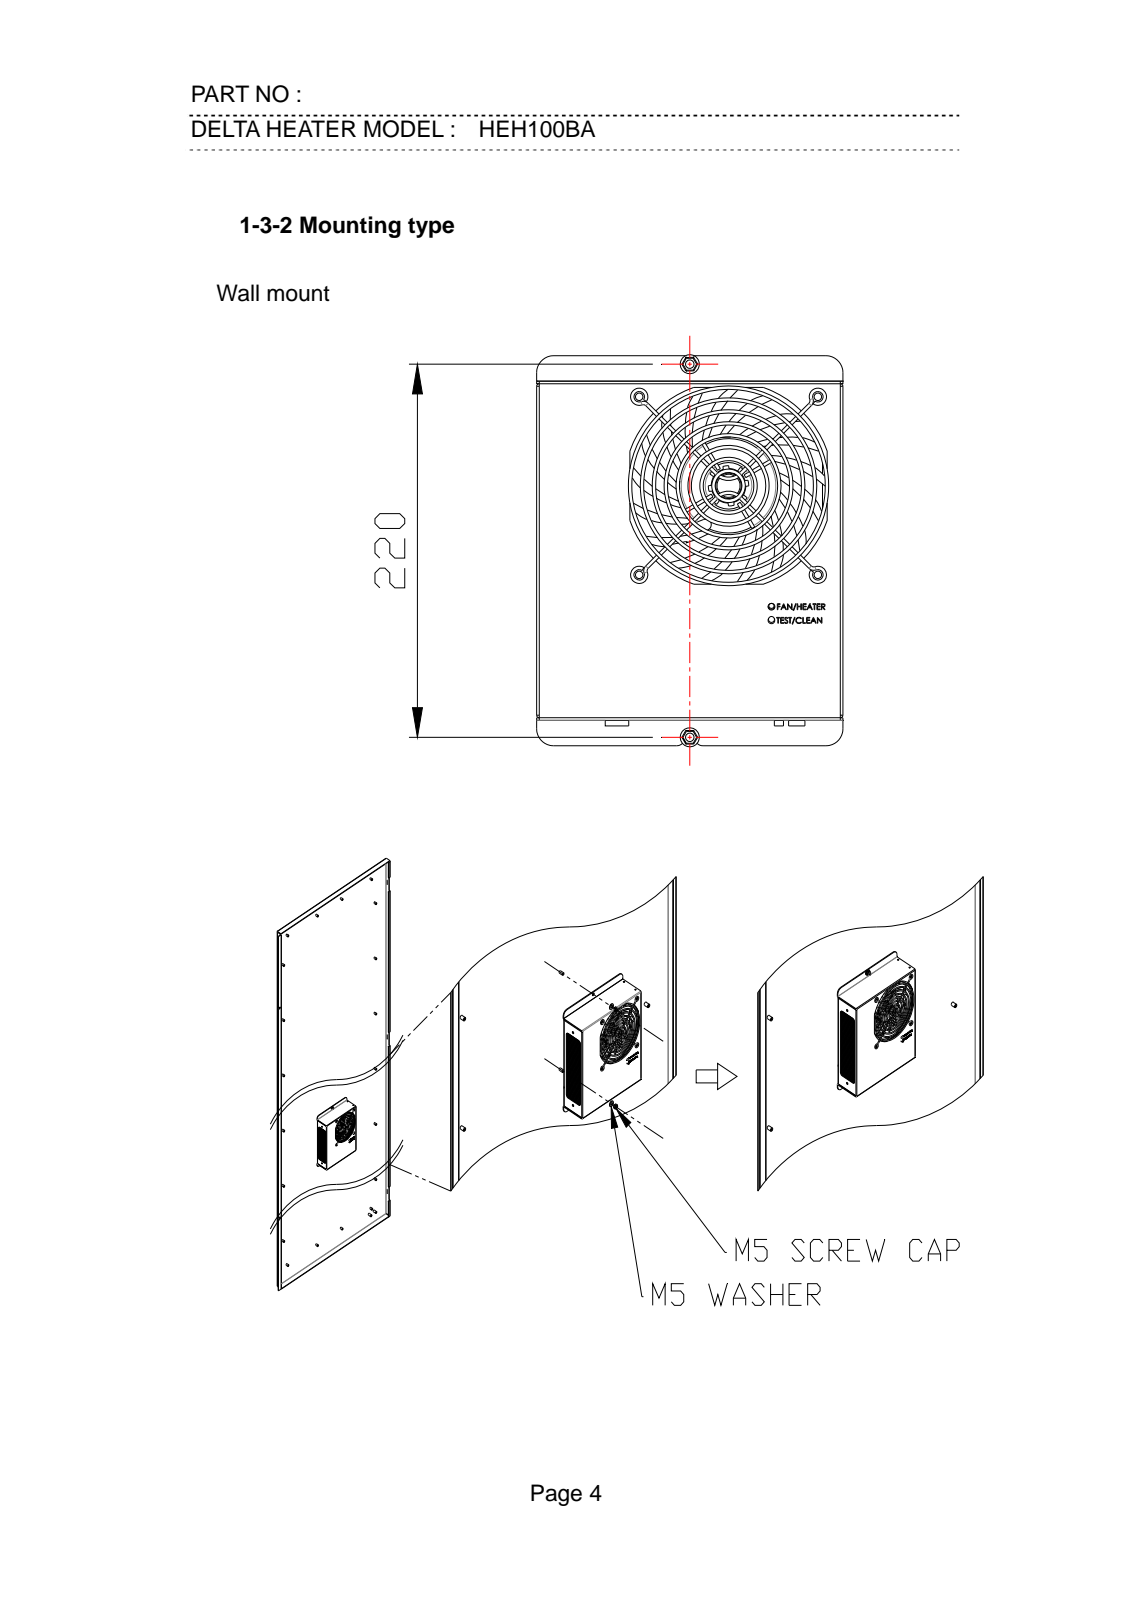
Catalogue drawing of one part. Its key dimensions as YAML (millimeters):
part_name: "HEH100BA"
step_written_by: "SolidWorks 2013 (CONFIG_CONTROL_DESIGN)"
units: millimeters
bodies: {solids: 89, faces: 4045, planar: 3343, cylindrical: 486, other: 216}
overall_size: [230, 185, 61.98]
volume: 302471
surface_area: 559569
round_holes:
  - {diameter: 4.2, count: 7}
  - {diameter: 6, count: 6}
  - {diameter: 3, count: 4}
  - {diameter: 4.4, count: 4}
  - {diameter: 4.5, count: 4}
  - {diameter: 2, count: 3}
  - {diameter: 4.33, count: 2}
  - {diameter: 1.97, count: 1}
  - {diameter: 3.6, count: 1}
  - {diameter: 5.5, count: 1}
  - {diameter: 13.6, count: 1}
  - {diameter: 15, count: 1}
round_bosses_or_shafts:
  - {diameter: 0.74, count: 8}
  - {diameter: 6.4, count: 4}
  - {diameter: 2, count: 4}
  - {diameter: 1.2, count: 4}
  - {diameter: 120, count: 1}
  - {diameter: 60, count: 1}
  - {diameter: 18, count: 1}
  - {diameter: 15, count: 1}
partial_cylinders:
  - {radius: 1.51, count: 18}
  - {radius: 0.5, count: 16}
  - {radius: 1, count: 16}
  - {radius: 5, count: 12}
  - {radius: 0.93, count: 4}
  - {radius: 1.25, count: 4}
  - {radius: 1.62, count: 4}
  - {radius: 2, count: 4}
face_to_face_distances: [1.5, 56.5, 55, 58, 203.5, 51.5, 3, 2, 5, 51]
hole_center_spacings: [105, 74.25, 35, 65, 91.31, 130, 145.34, 148.49]
